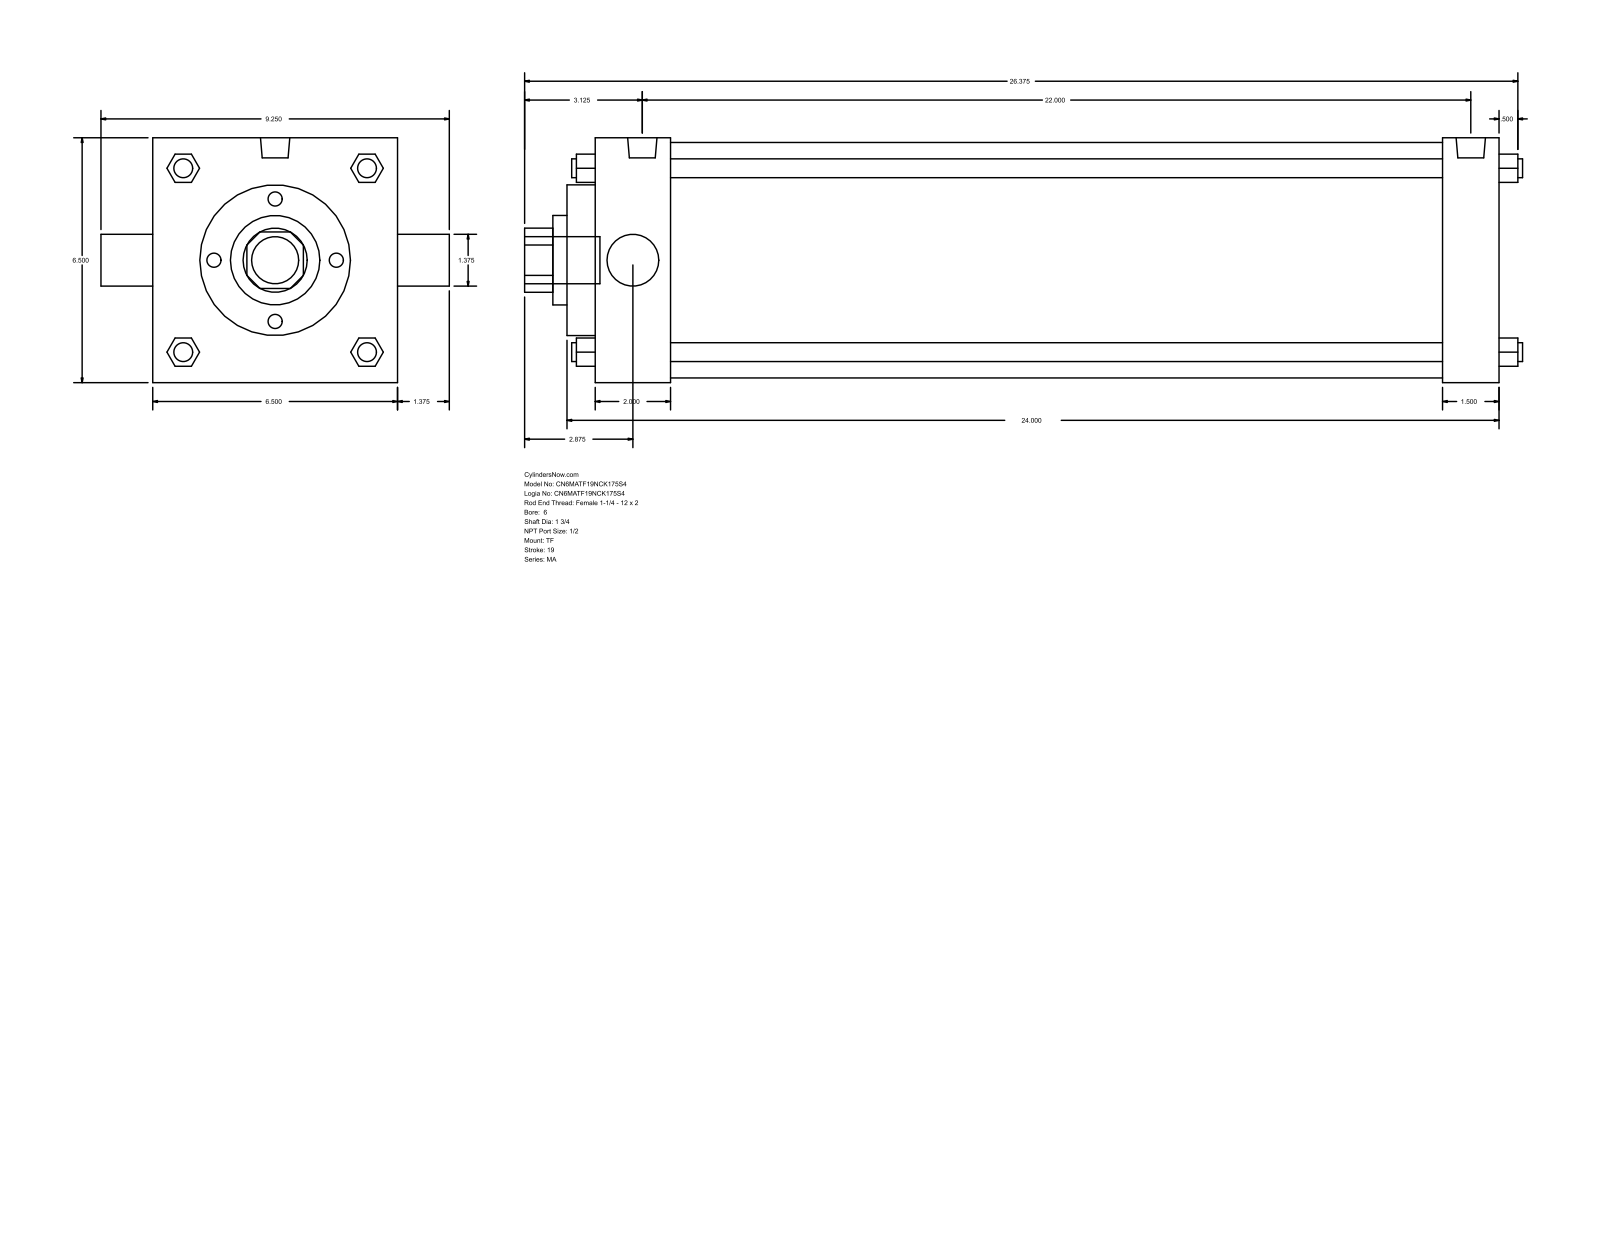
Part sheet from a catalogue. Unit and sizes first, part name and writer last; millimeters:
Units: millimetres
Overall size (bounding box): 673.1 × 234.95 × 165.1
Round holes (diameter × count): ⌀34.92 ×1, ⌀44.45 ×1, ⌀60.33 ×1, ⌀101.6 ×1, ⌀158.75 ×1
Round bosses / shafts (diameter × count): ⌀12.7 ×4, ⌀17.46 ×3, ⌀19.77 ×2, ⌀31.75 ×1
Partial cylindrical surfaces — rounded edges, fillets, slot ends (radius × count): R21.63 ×1
Main face-to-face distances: 165.1, 609.61, 19.05, 50.8, 571.5, 558.81, 520.7, 38.11, 69.85, 590.55
Bodies: 0 solids, 122 faces (93 planar, 29 cylindrical, 0 other)
Part name (STEP PRODUCT): MA_TF__0600_1.75
STEP written by: GSSL Pune (CONFIG_CONTROL_DESIGN)
